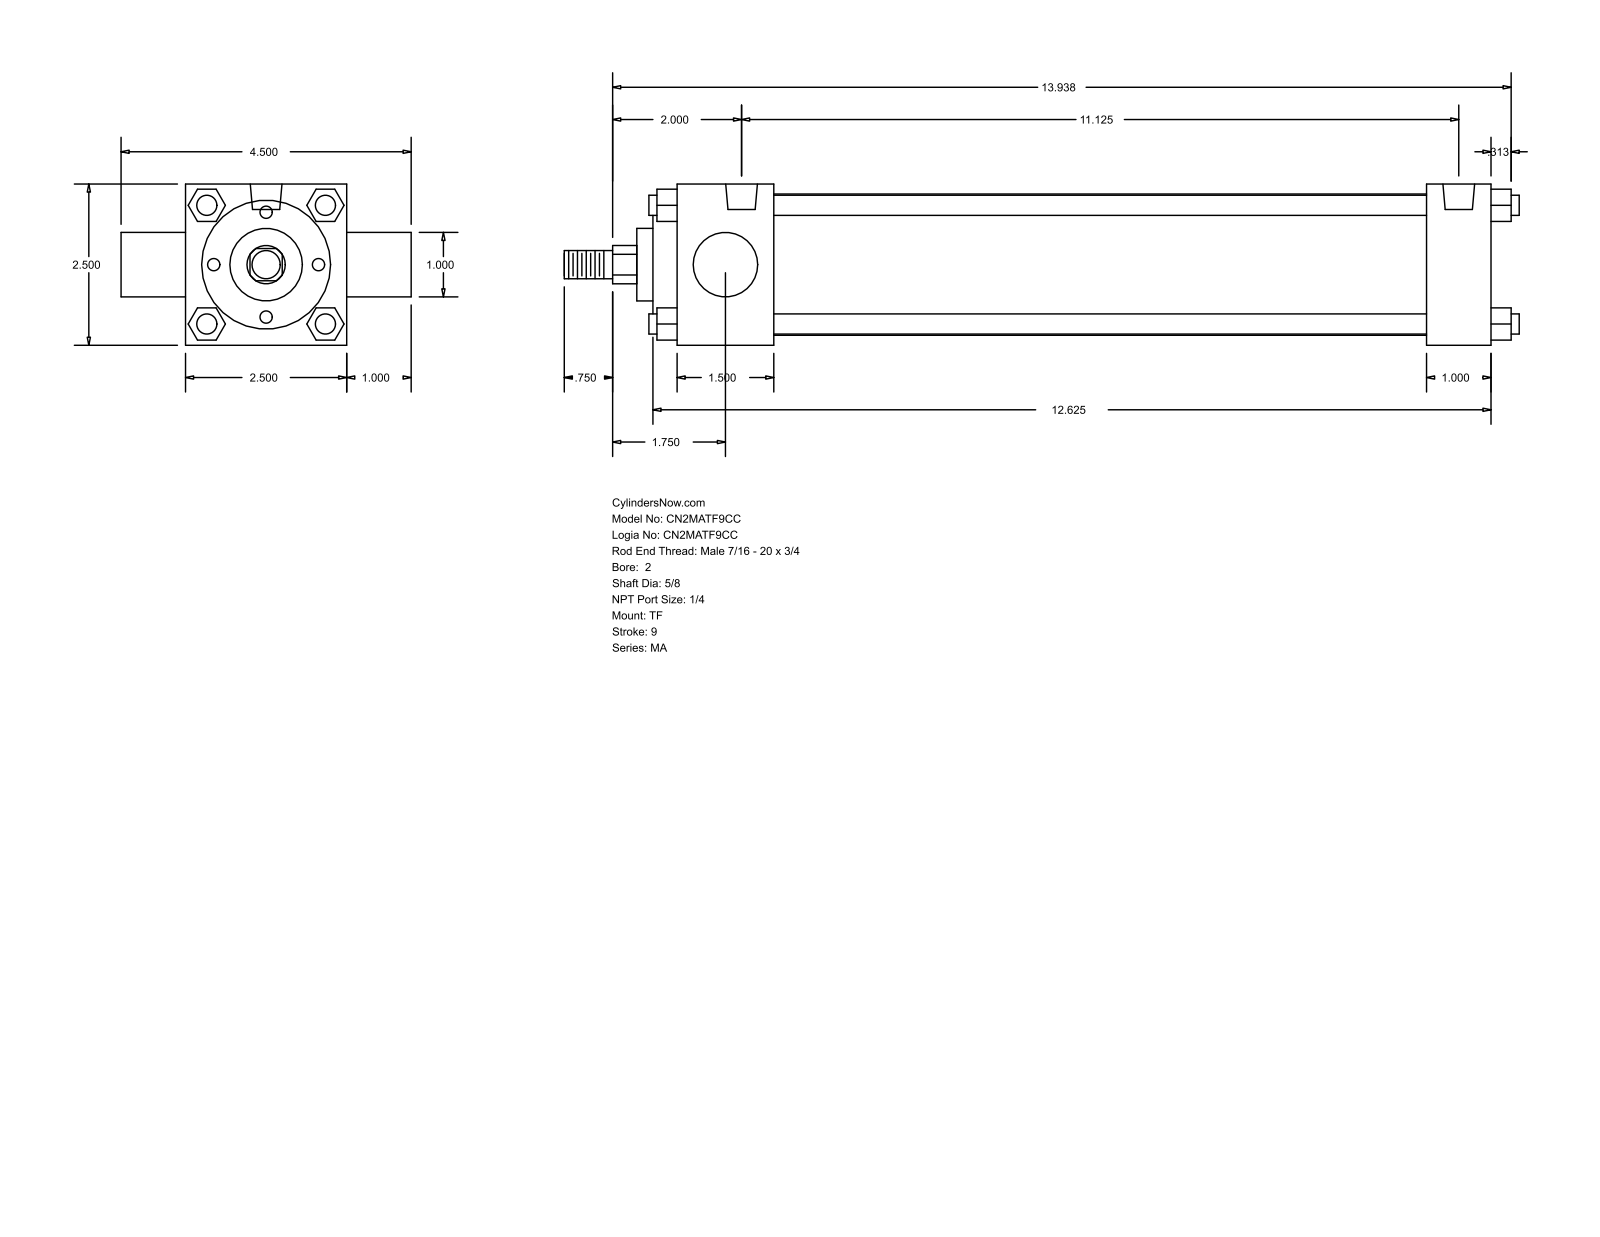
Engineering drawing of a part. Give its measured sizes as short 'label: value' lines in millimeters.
name: MA_TF__0200_0.625
written by: GSSL Pune (CONFIG_CONTROL_DESIGN)
unit: mm
bodies: 0 solids, 122 faces (93 planar, 29 cylindrical, 0 other)
size: 376.24 × 114.3 × 63.5
holes: 3× ⌀7.94, 2× ⌀12.49
bosses: 4× ⌀7.94, 1× ⌀55.63, 1× ⌀50.8, 1× ⌀28.57, 1× ⌀25.4, 1× ⌀15.88, 1× ⌀11.11
rounds: 1× R7.54
face distances: 63.5, 38.1, 12.7, 320.67, 295.28, 257.18, 282.57, 25.39, 9.52, 47.62
hole spacings: 282.58
